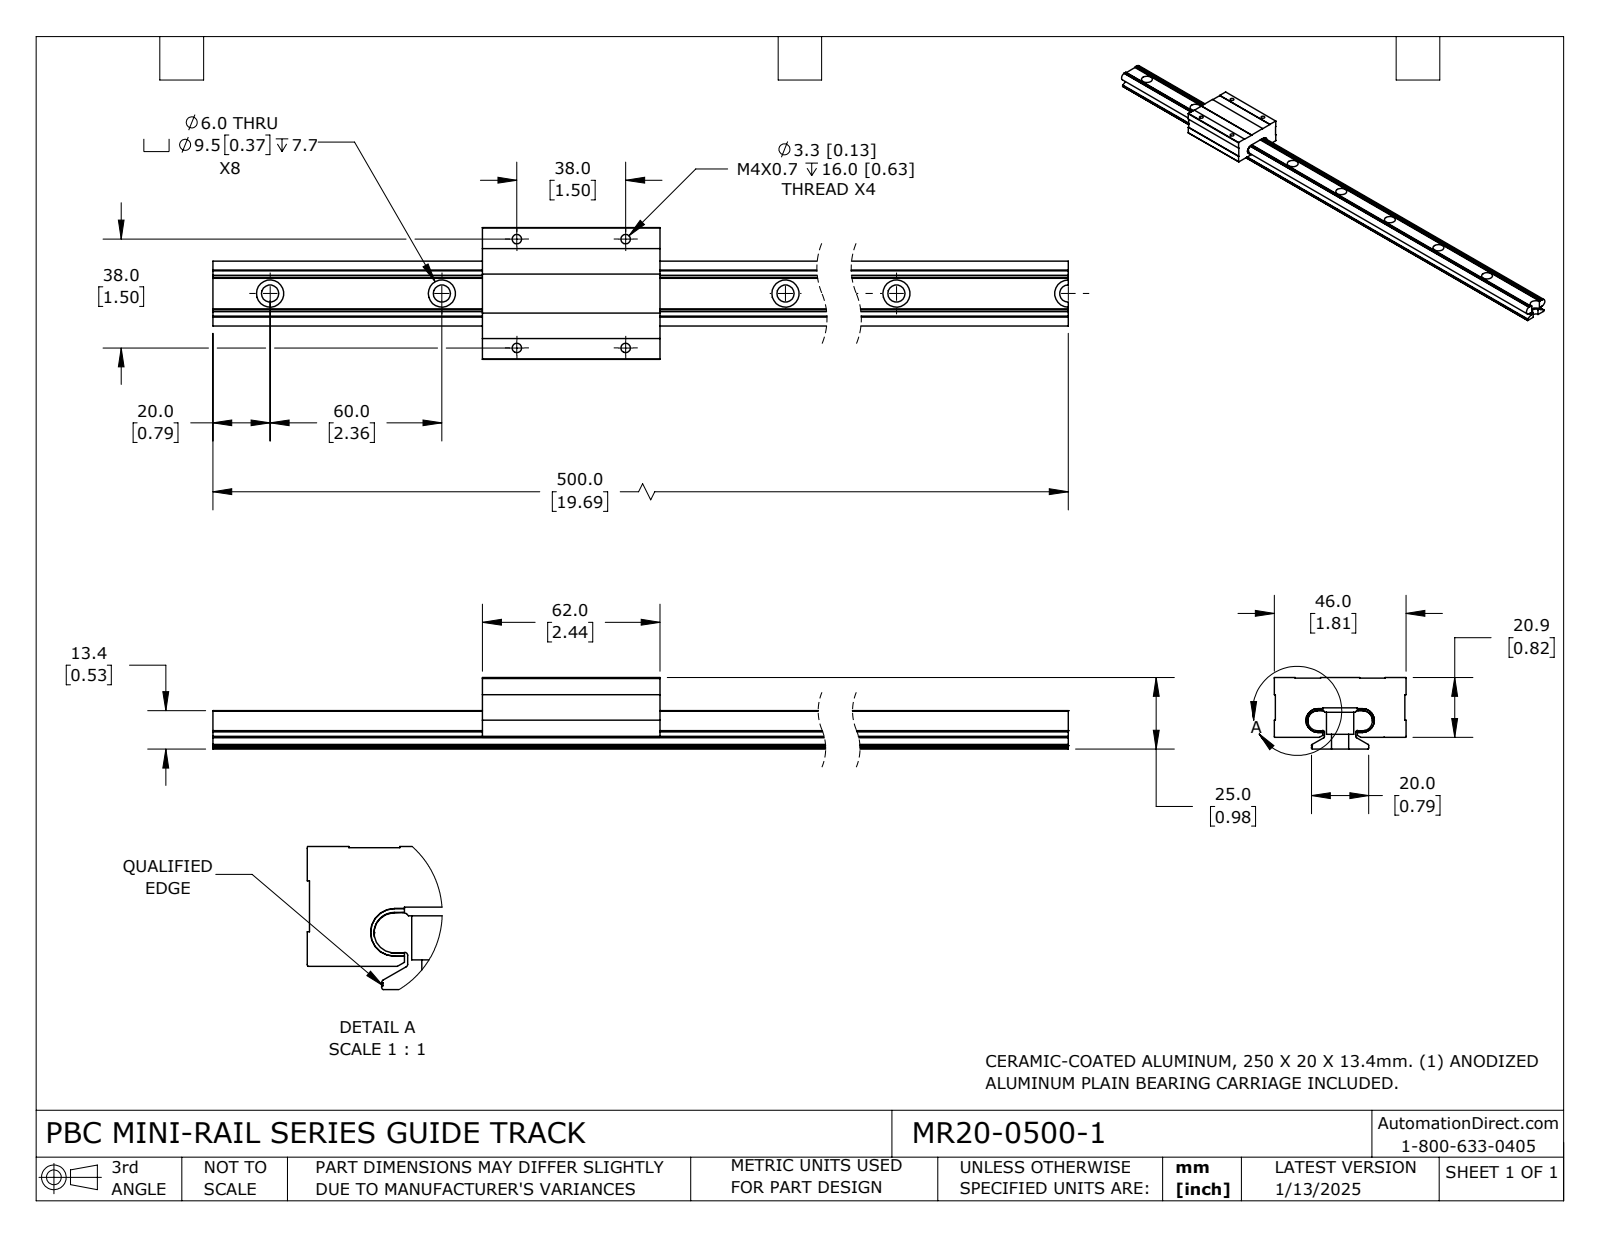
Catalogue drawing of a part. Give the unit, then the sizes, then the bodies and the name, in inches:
Units: inches
Overall size (bounding box): 19.685 × 1.811 × 0.984
Round holes (diameter × count): ⌀0.236 ×8, ⌀0.374 ×8, ⌀0.13 ×4
Partial cylindrical surfaces — rounded edges, fillets, slot ends (radius × count): R0.02 ×10, R0.14 ×4, R0.04 ×2, R0.138 ×2, R0.138 ×2, R0.164 ×2, R0.005 ×1, R0.118 ×1
Main face-to-face distances: 0.507, 0.16, 0.347, 0.984, 0.824, 0.477, 0.691, 1.12, 0.296, 0.976
Hole centre spacings: 2.362, 4.724, 7.087, 9.449, 11.811, 0.766, 1.274, 1.496
Volume: 9.726 in³ · Surface area: 92.92 in²
Bodies: 4 solids, 160 faces (87 planar, 73 cylindrical, 0 other)
Part name (STEP PRODUCT): MR20-0500-1_RAIL; MR20-0500-1_CARRIAGE; MR20-0500-1
STEP written by: SolidWorks 2023 (CONFIG_CONTROL_DESIGN)
